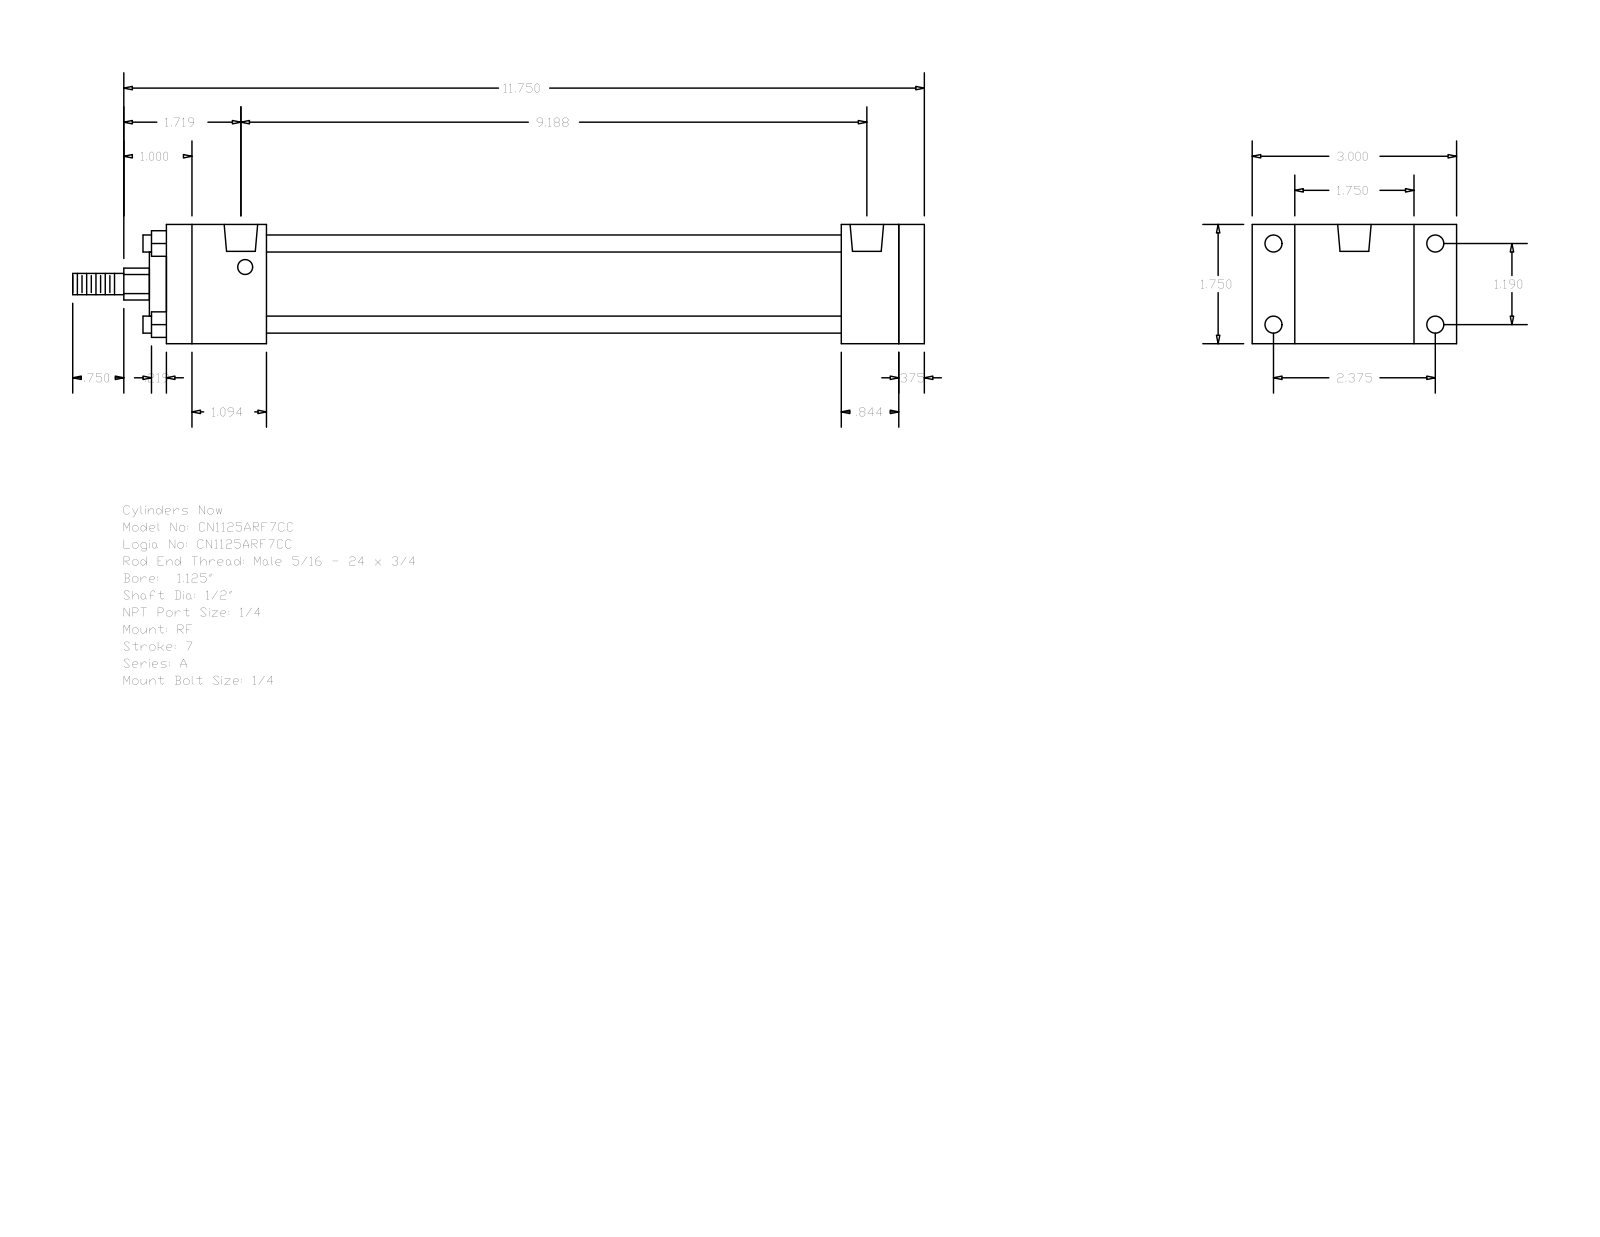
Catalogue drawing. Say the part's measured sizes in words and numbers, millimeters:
The part is named "A_RF__0112_0.5". Its 3-D file was written by "GSSL Pune (CONFIG_CONTROL_DESIGN)". It is 0 solids with 92 faces: 64 planar, 28 cylindrical and 0 other. Overall it measures 317.5 by 76.2 by 44.45 millimeters. Round holes: 4 of diameter 5.56, 4 of diameter 6.35, 2 of diameter 12.49. Round bosses or shafts: 4 of diameter 6.35, 1 of diameter 31.88, 1 of diameter 23.81, 1 of diameter 12.7, 1 of diameter 7.94. Partial cylindrical surfaces (rounded edges, fillets, slot ends): 1 of radius 5.94. The main face-to-face distances are 44.46, 9.52, 273.05, 282.57, 37.3, 251.61, 214.31, 235.75, 245.27, 21.44. The hole center spacings are 30.22, 60.32, 67.47, 230.19, 1.58, 1.59, 231.77, 231.78.
